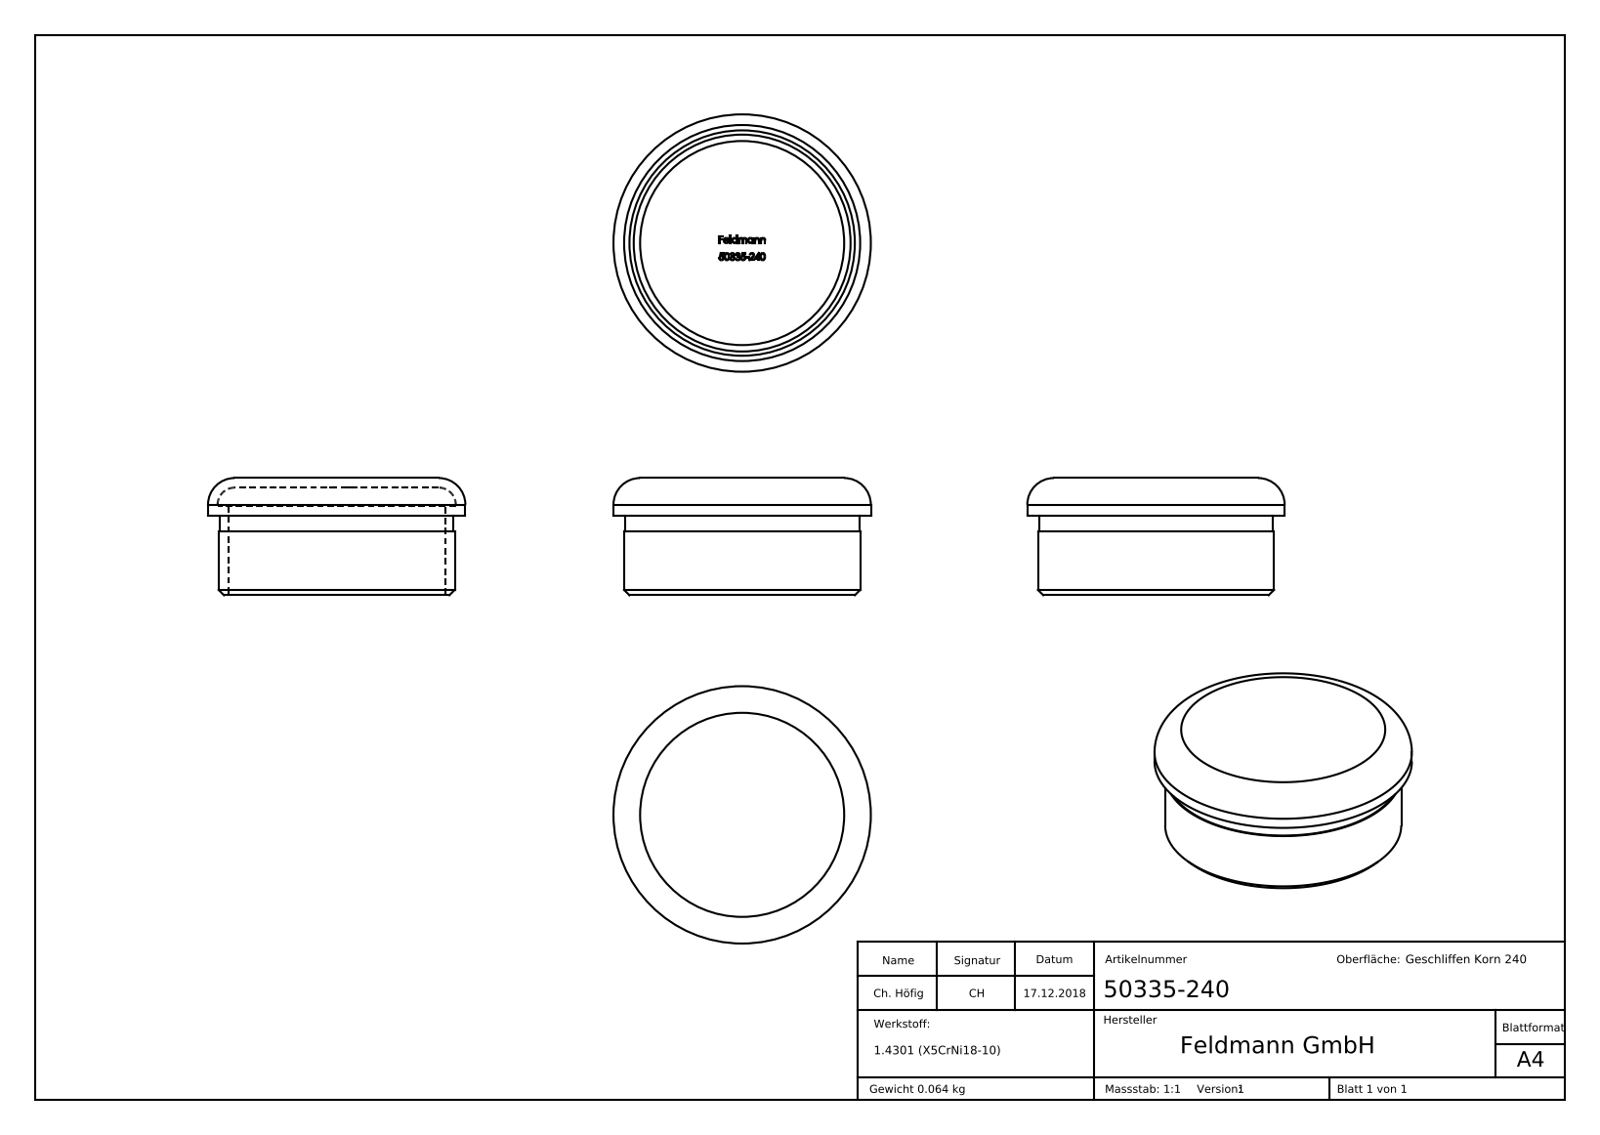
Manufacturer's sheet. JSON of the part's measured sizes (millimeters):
{"part_name": "50335-240", "step_written_by": "SolidWorks 2015 (CONFIG_CONTROL_DESIGN)", "units": "millimeters", "bodies": {"solids": 1, "faces": 254, "planar": 124, "cylindrical": 8, "other": 122}, "overall_size": [48.3, 48.3, 22], "volume_mm3": 8123, "surface_area_mm2": 9420, "round_holes": [[40.7, 1]], "round_bosses_or_shafts": [[48.3, 1], [44.3, 1], [43.9, 1]], "face_to_face_distances": [1.8, 5.2, 7, 3.4, 15, 16.8, 20.2, 22, 12, 3]}
